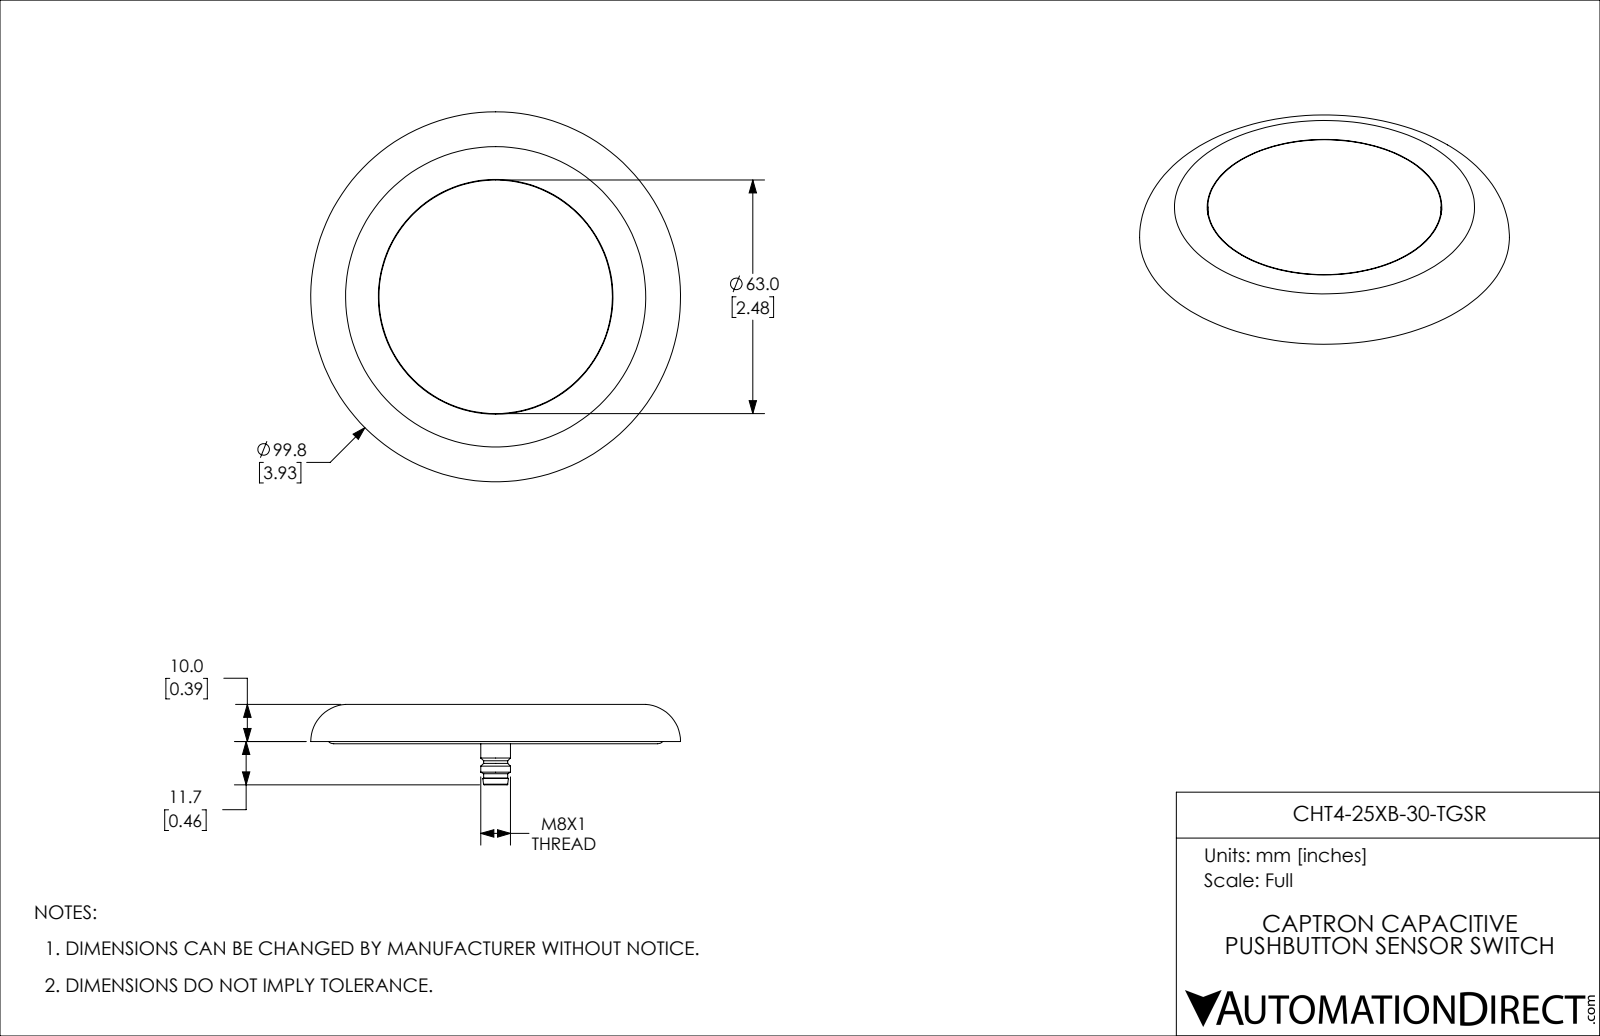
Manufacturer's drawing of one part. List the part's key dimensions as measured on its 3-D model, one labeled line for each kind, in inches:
Part name (STEP PRODUCT): CHT4-25XB-30-TGSR
STEP written by: SolidWorks 2019 (CONFIG_CONTROL_DESIGN)
Units: inches
Bodies: 9 solids, 106 faces (25 planar, 35 cylindrical, 46 other)
Overall size (bounding box): 3.929 × 3.929 × 0.854
Volume: 1.761 in³ · Surface area: 64 in²
Round holes (diameter × count): ⌀0.228 ×1, ⌀2.299 ×1, ⌀2.493 ×1, ⌀2.543 ×1
Round bosses / shafts (diameter × count): ⌀0.039 ×5, ⌀2.48 ×1, ⌀0.315 ×1, ⌀0.256 ×1
Partial cylindrical surfaces — rounded edges, fillets, slot ends (radius × count): R0.02 ×2, R0.039 ×1, R1.26 ×1
Main face-to-face distances: 0.326, 0.056, 0.382, 0.057, 0.324, 0.269, 0.057, 0.064, 0.332, 0.39
Hole centre spacings: 0.126
